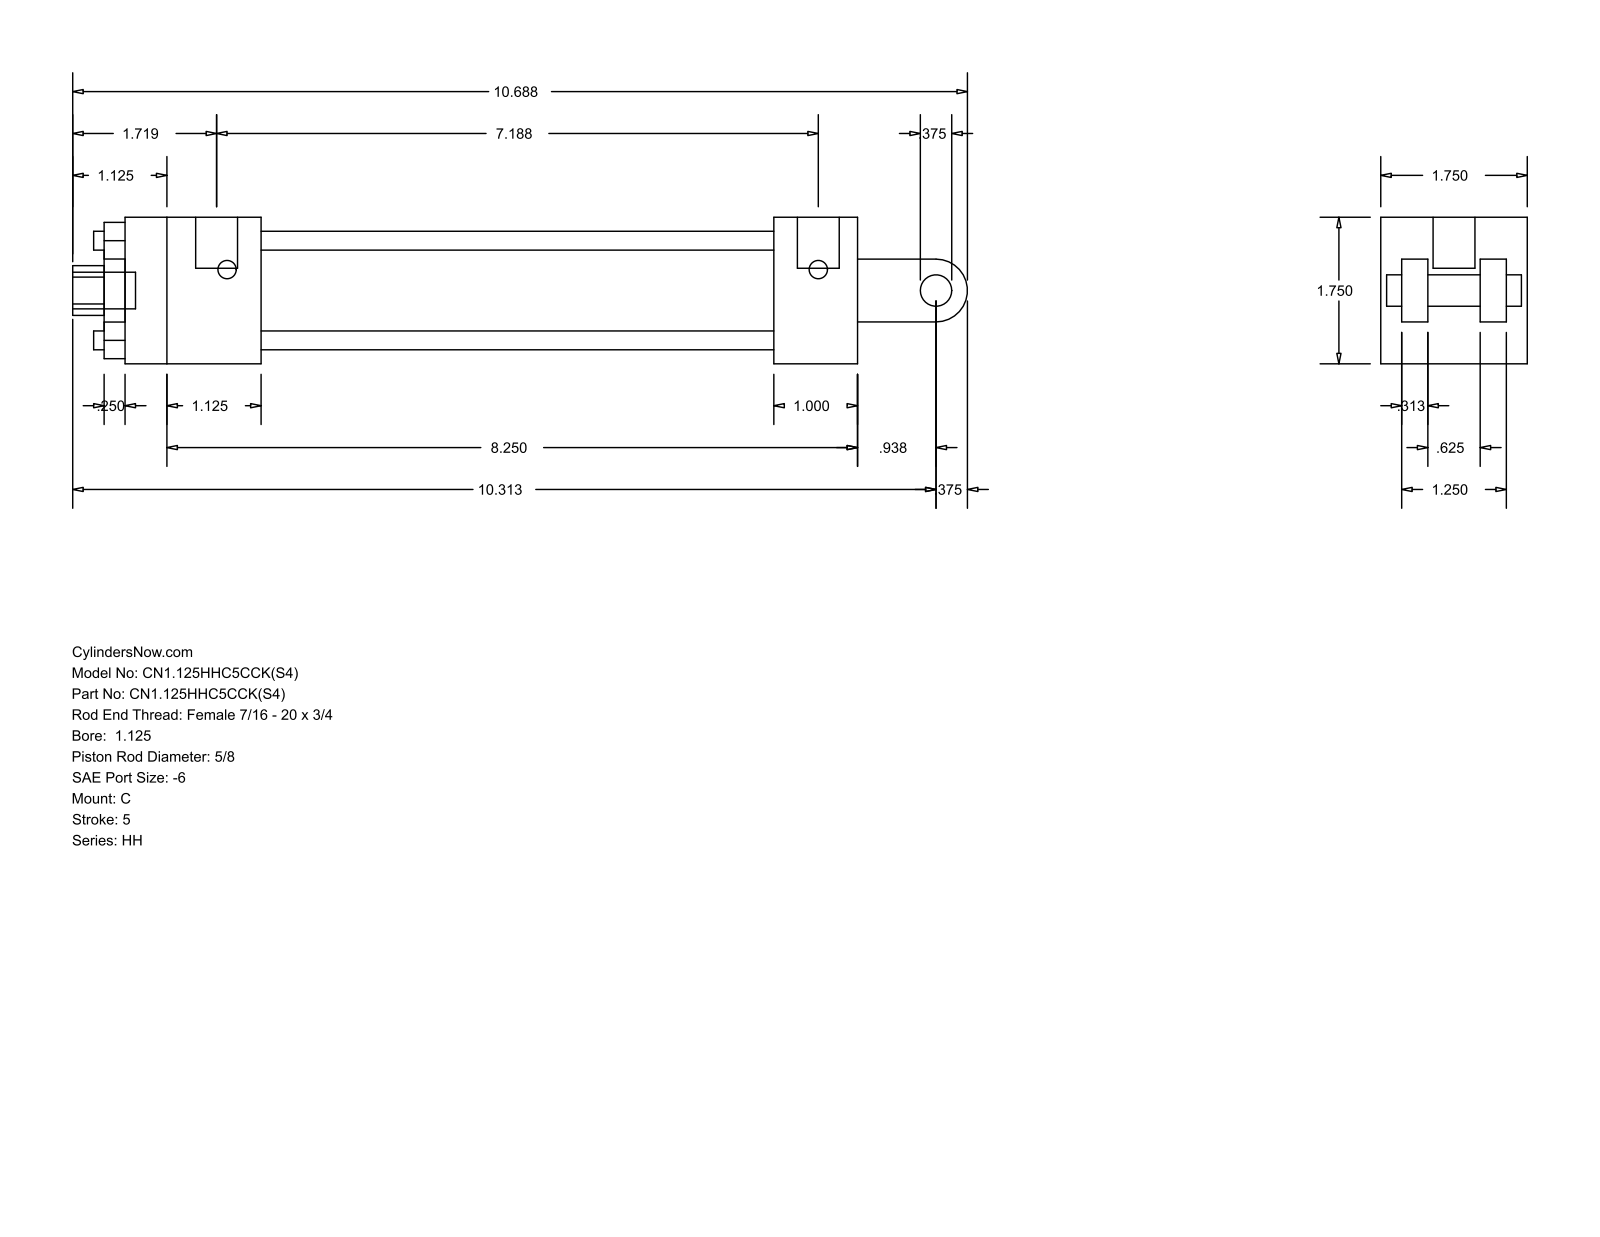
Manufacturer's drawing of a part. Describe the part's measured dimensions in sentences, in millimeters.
The part is named "HH_C__0112_0.625". Its 3-D file was written by "GSSL Pune (CONFIG_CONTROL_DESIGN)". It is 0 solids with 99 faces: 70 planar, 29 cylindrical and 0 other. Overall it measures 271.46 by 44.45 by 44.45 millimeters. Round holes: 4 of diameter 5.71, 2 of diameter 5.56, 1 of diameter 12.7, 1 of diameter 15.88, 1 of diameter 28.57, 1 of diameter 34.92. Round bosses or shafts: 2 of diameter 5.56, 1 of diameter 12.7, 1 of diameter 11.11, 1 of diameter 9.53. Partial cylindrical surfaces (rounded edges, fillets, slot ends): 1 of radius 7.54, 1 of radius 9.53. The main face-to-face distances are 44.46, 6.35, 31.76, 14.29, 12.7, 30.17, 38.11, 7.94, 23.82, 25.4. The hole center spacings are 21.37, 30.22, 42.74.
